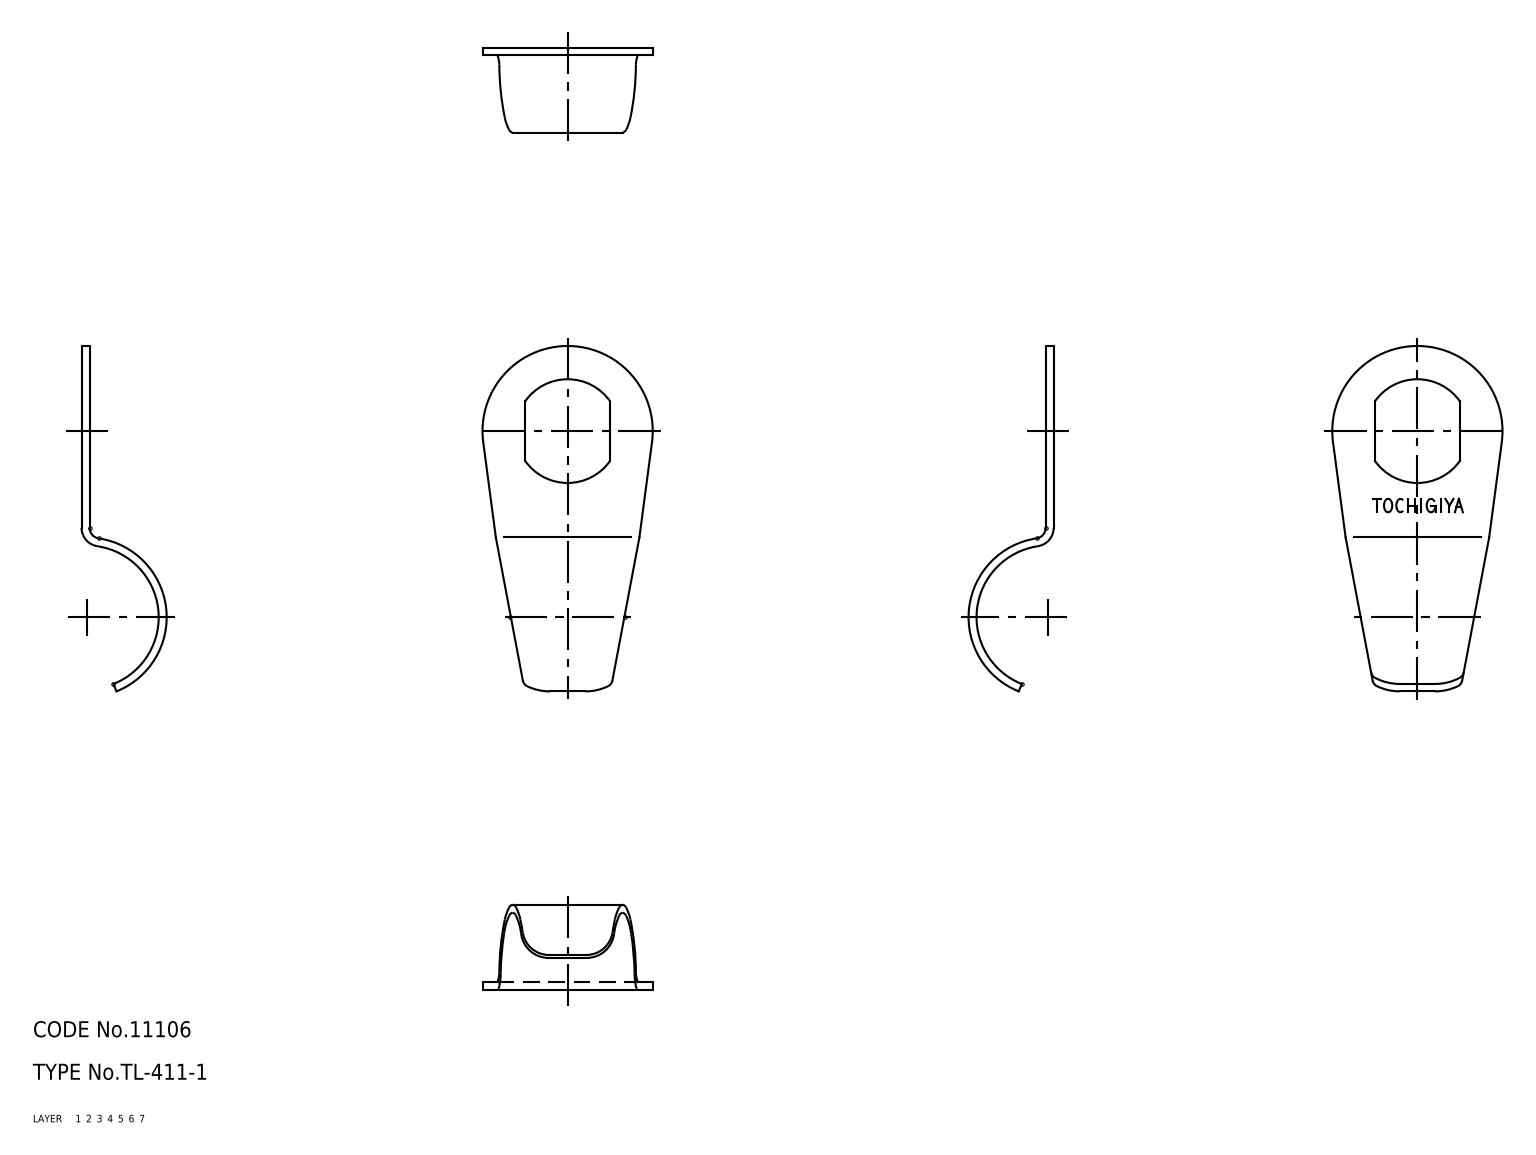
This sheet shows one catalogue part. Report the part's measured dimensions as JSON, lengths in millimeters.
{"part_name": "TL_411_1; lever", "step_written_by": "SolidWorks 2015 (AUTOMOTIVE_DESIGN)", "units": "millimeters", "bodies": {"solids": 1, "faces": 19, "planar": 7, "cylindrical": 12, "other": 0}, "overall_size": [64.93, 32, 16], "volume_mm3": 2318, "surface_area_mm2": 3454, "partial_cylinders_radius": [[5, 2], [2, 1], [3.5, 1], [9.75, 1], [13.5, 1], [15, 1], [16, 1]], "face_to_face_distances": [1.5, 16]}
